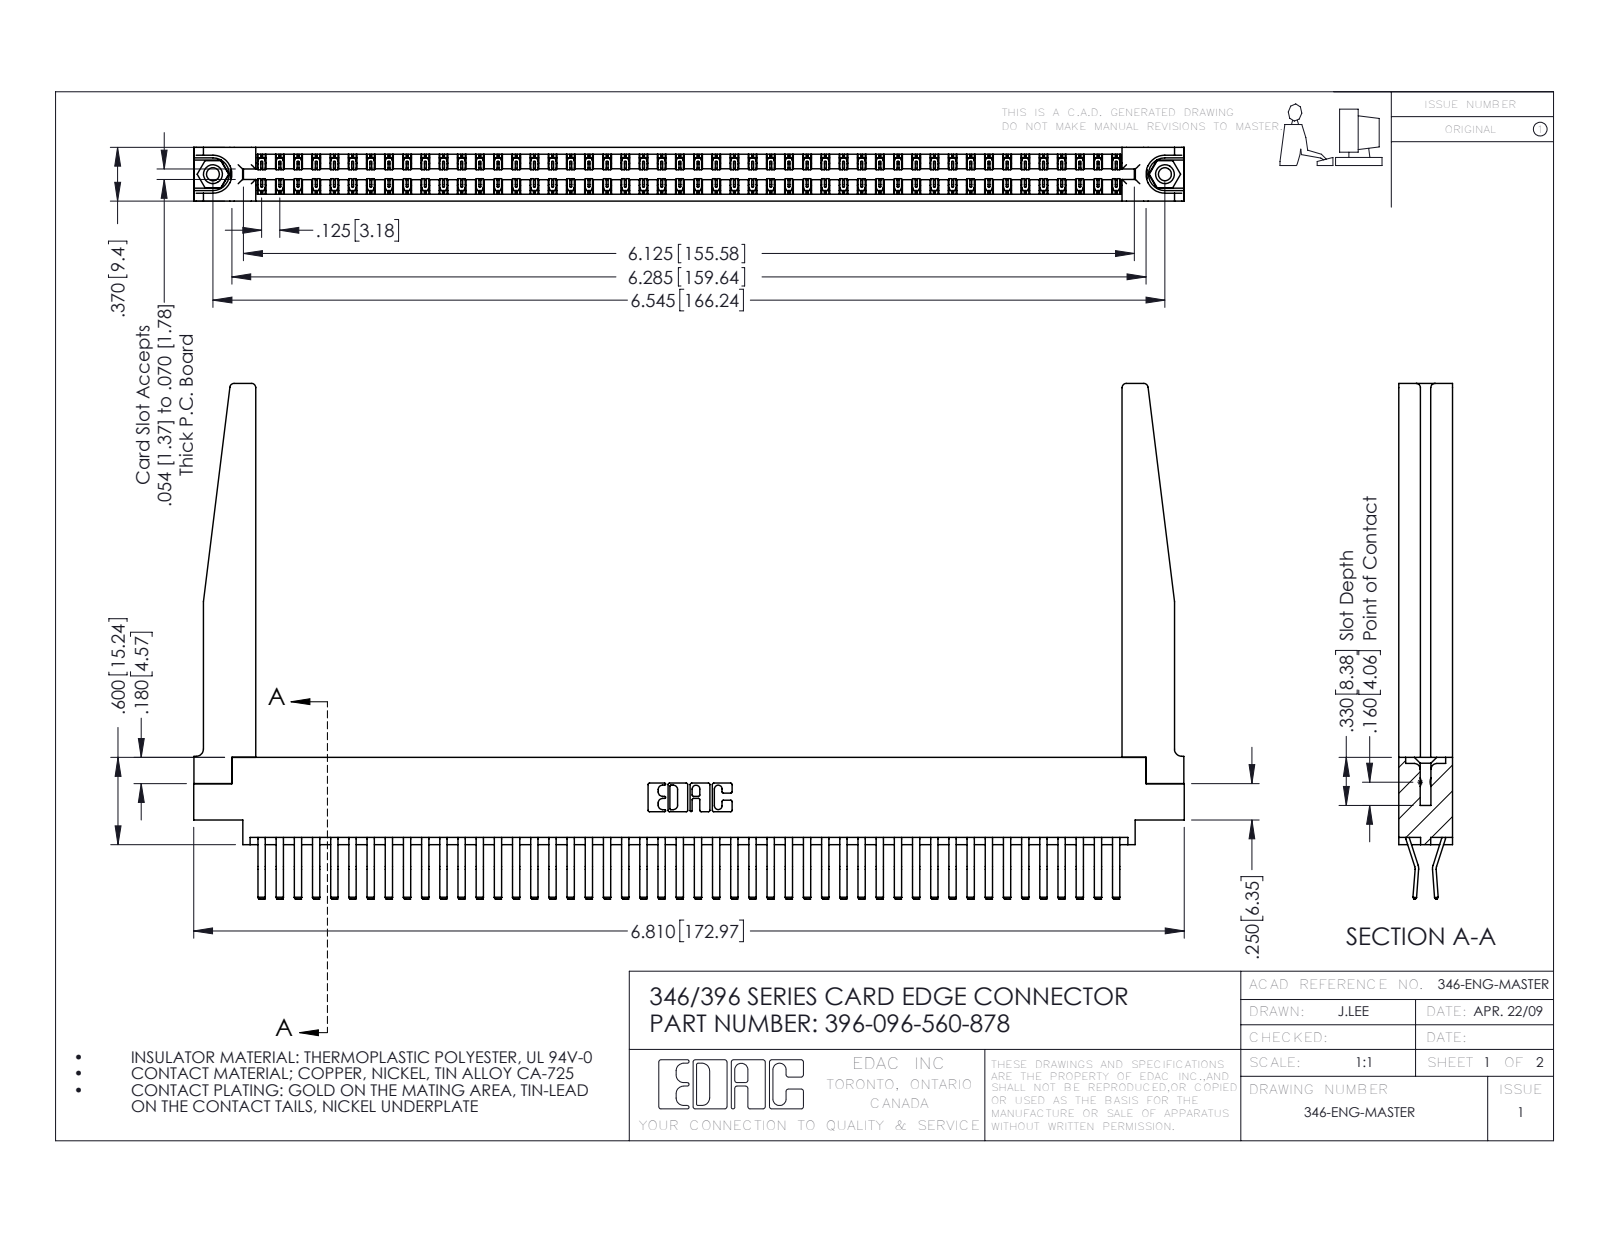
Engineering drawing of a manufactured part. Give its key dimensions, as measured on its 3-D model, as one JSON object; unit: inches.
{"part_name": "346 Part_0.170 Offset - 0.156 Dia-TH; 396-096-560-878; 345-250-001_345-250-001-102; 346-220-078_345-220-078 (+1 more)", "step_written_by": "SolidWorks 2016 (CONFIG_CONTROL_DESIGN)", "units": "inches", "bodies": {"solids": 101, "faces": 5544, "planar": 3582, "cylindrical": 1910, "other": 52}, "overall_size": [6.81, 3.545, 0.37], "volume_in3": 1.483, "surface_area_in2": 50.21, "round_holes": [[0.089, 2], [0.125, 2], [0.156, 2], [0.064, 1]], "round_bosses_or_shafts": [[0.155, 2]], "partial_cylinders_radius": [[0.006, 144], [0.01, 22], [0.03, 8], [0.007, 6], [0.031, 6], [0.05, 4], [0.026, 3], [0.01, 2]], "face_to_face_distances": [0.37, 0.048, 0.322, 0.025, 0.072, 0.148, 0.15, 0.25, 0.298, 0.275], "hole_center_spacings": [0.246, 6.336, 6.545]}
